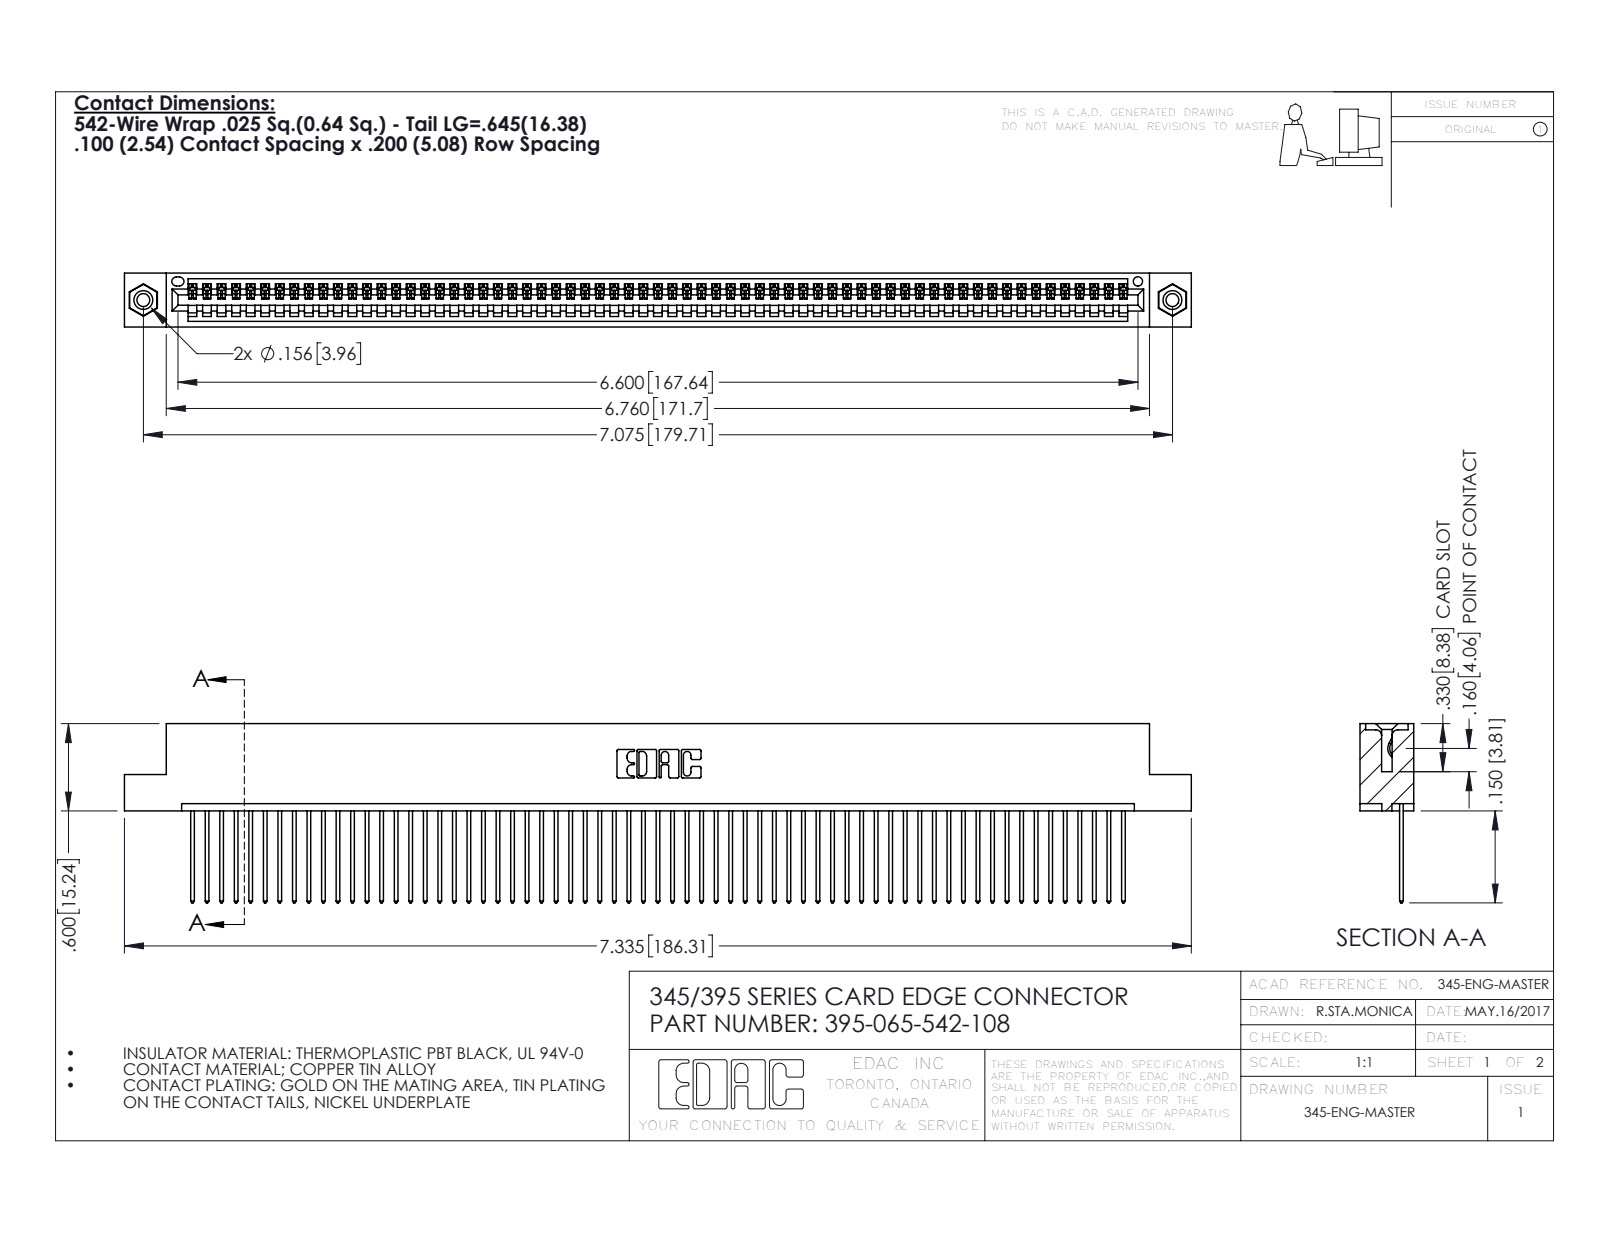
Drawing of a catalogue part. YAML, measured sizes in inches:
part_name: "395-065-542-108; 345-292-001_345-293-142; 345-250-001_345-250-003-102; 345 Part_Flush Mounting Lugs - 0.156 Dia-TI"
step_written_by: "SolidWorks 2016 (CONFIG_CONTROL_DESIGN)"
units: inches
bodies: {solids: 68, faces: 3956, planar: 2712, cylindrical: 1228, other: 16}
overall_size: [7.335, 1.232, 0.37]
volume: 1.1
surface_area: 39.05
round_holes:
  - {diameter: 0.089, count: 2}
  - {diameter: 0.125, count: 2}
  - {diameter: 0.156, count: 2}
  - {diameter: 0.064, count: 1}
round_bosses_or_shafts:
  - {diameter: 0.155, count: 2}
partial_cylinders:
  - {radius: 0.006, count: 130}
  - {radius: 0.01, count: 130}
  - {radius: 0.01, count: 22}
  - {radius: 0.007, count: 6}
  - {radius: 0.031, count: 6}
  - {radius: 0.026, count: 3}
  - {radius: 0.031, count: 2}
  - {radius: 0.04, count: 2}
face_to_face_distances: [0.072, 0.298, 0.098, 0.272, 0.025, 0.37, 0.2, 0.225, 0.149, 0.072]
hole_center_spacings: [0.27, 6.839, 7.075]
